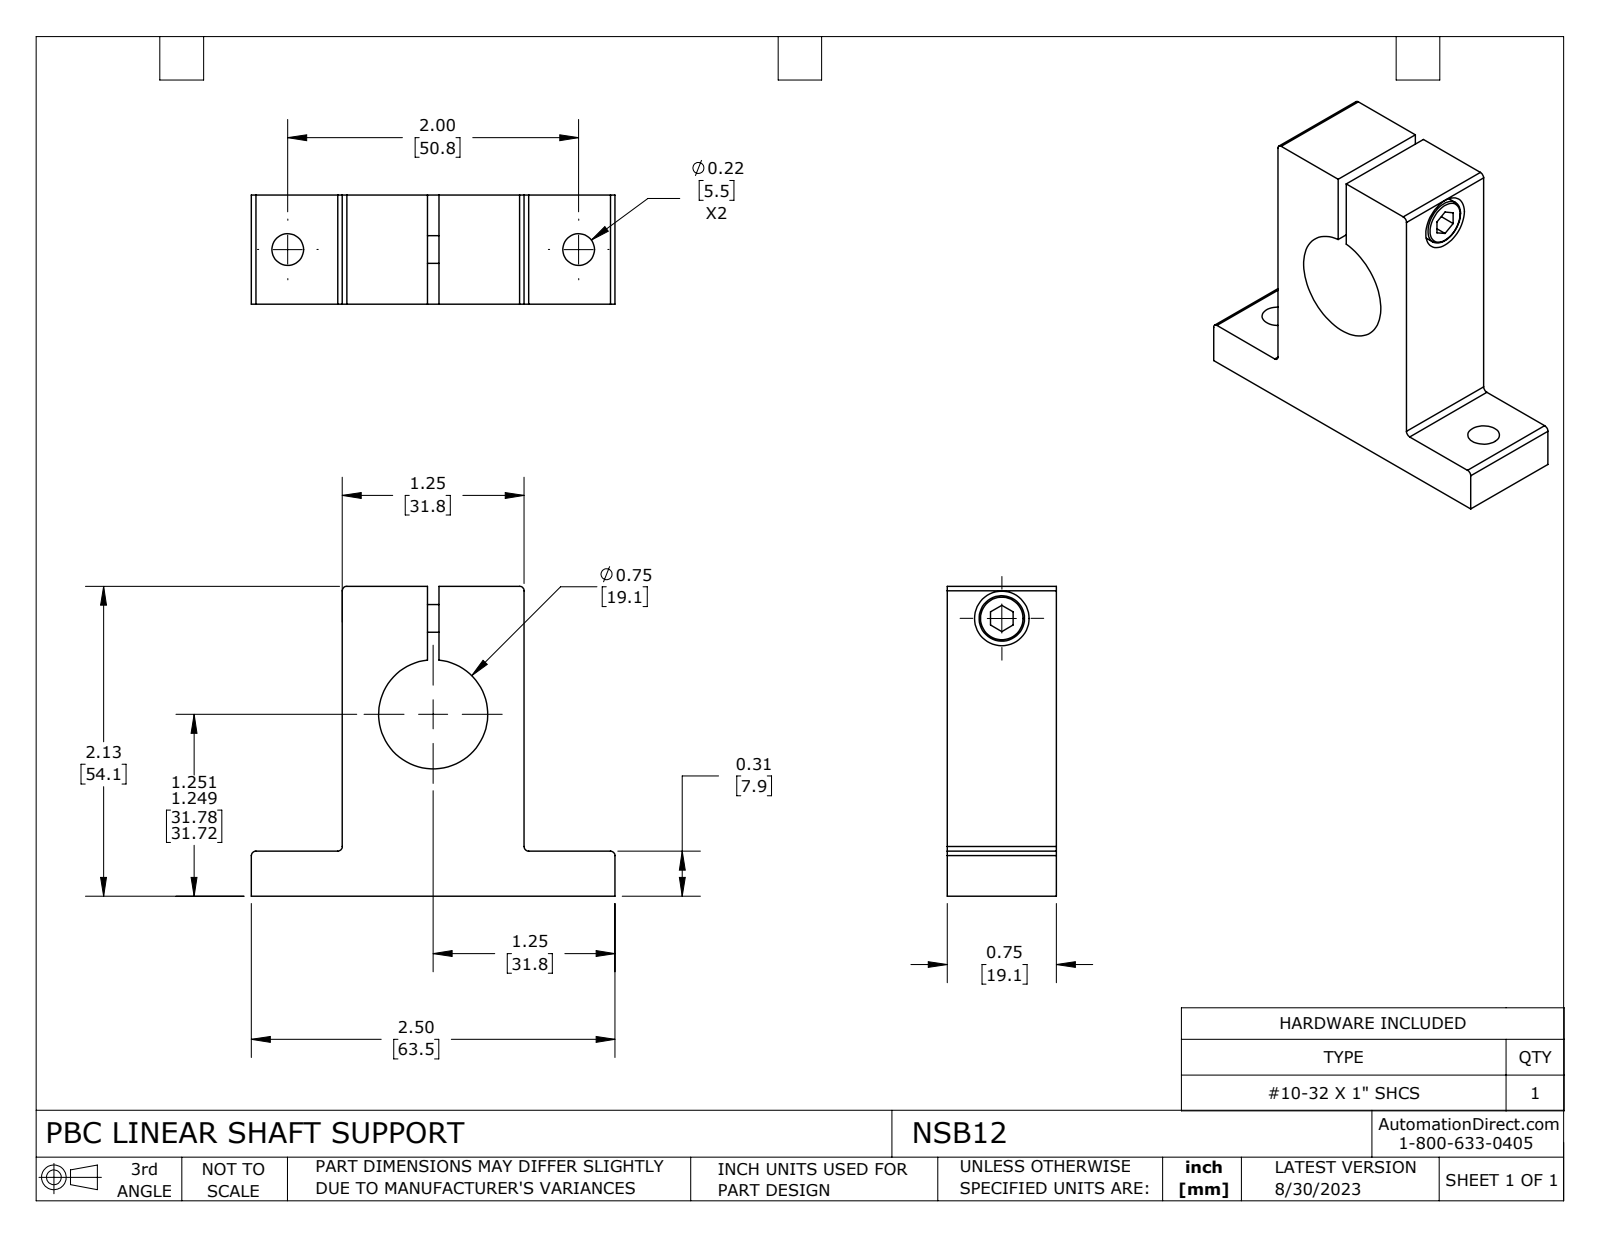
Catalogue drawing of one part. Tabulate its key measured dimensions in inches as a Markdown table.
| quantity | value |
| --- | --- |
| part name | NSB12 |
| STEP written by | SolidWorks 2023 (CONFIG_CONTROL_DESIGN) |
| units | inches |
| bodies | 2 solids, 51 faces (24 planar, 23 cylindrical, 4 other) |
| overall size | 2.5 × 2.13 × 0.75 |
| volume | 1.899 in³ |
| surface area | 16.35 in² |
| round holes (diameter × count) | 0.218 × 2, 0.15 × 1, 0.201 × 1, 0.375 × 1, 0.75 × 1 |
| round bosses / shafts (diameter × count) | 0.313 × 1, 0.19 × 1 |
| partial cylindrical surfaces (radius × count) | 0.031 × 6 |
| main face-to-face distances | 0.75, 1.25, 2.13, 0.31, 1.82, 0.586, 0.665, 0.625, 1.211, 1.289 |
| hole center spacings | 2 |
